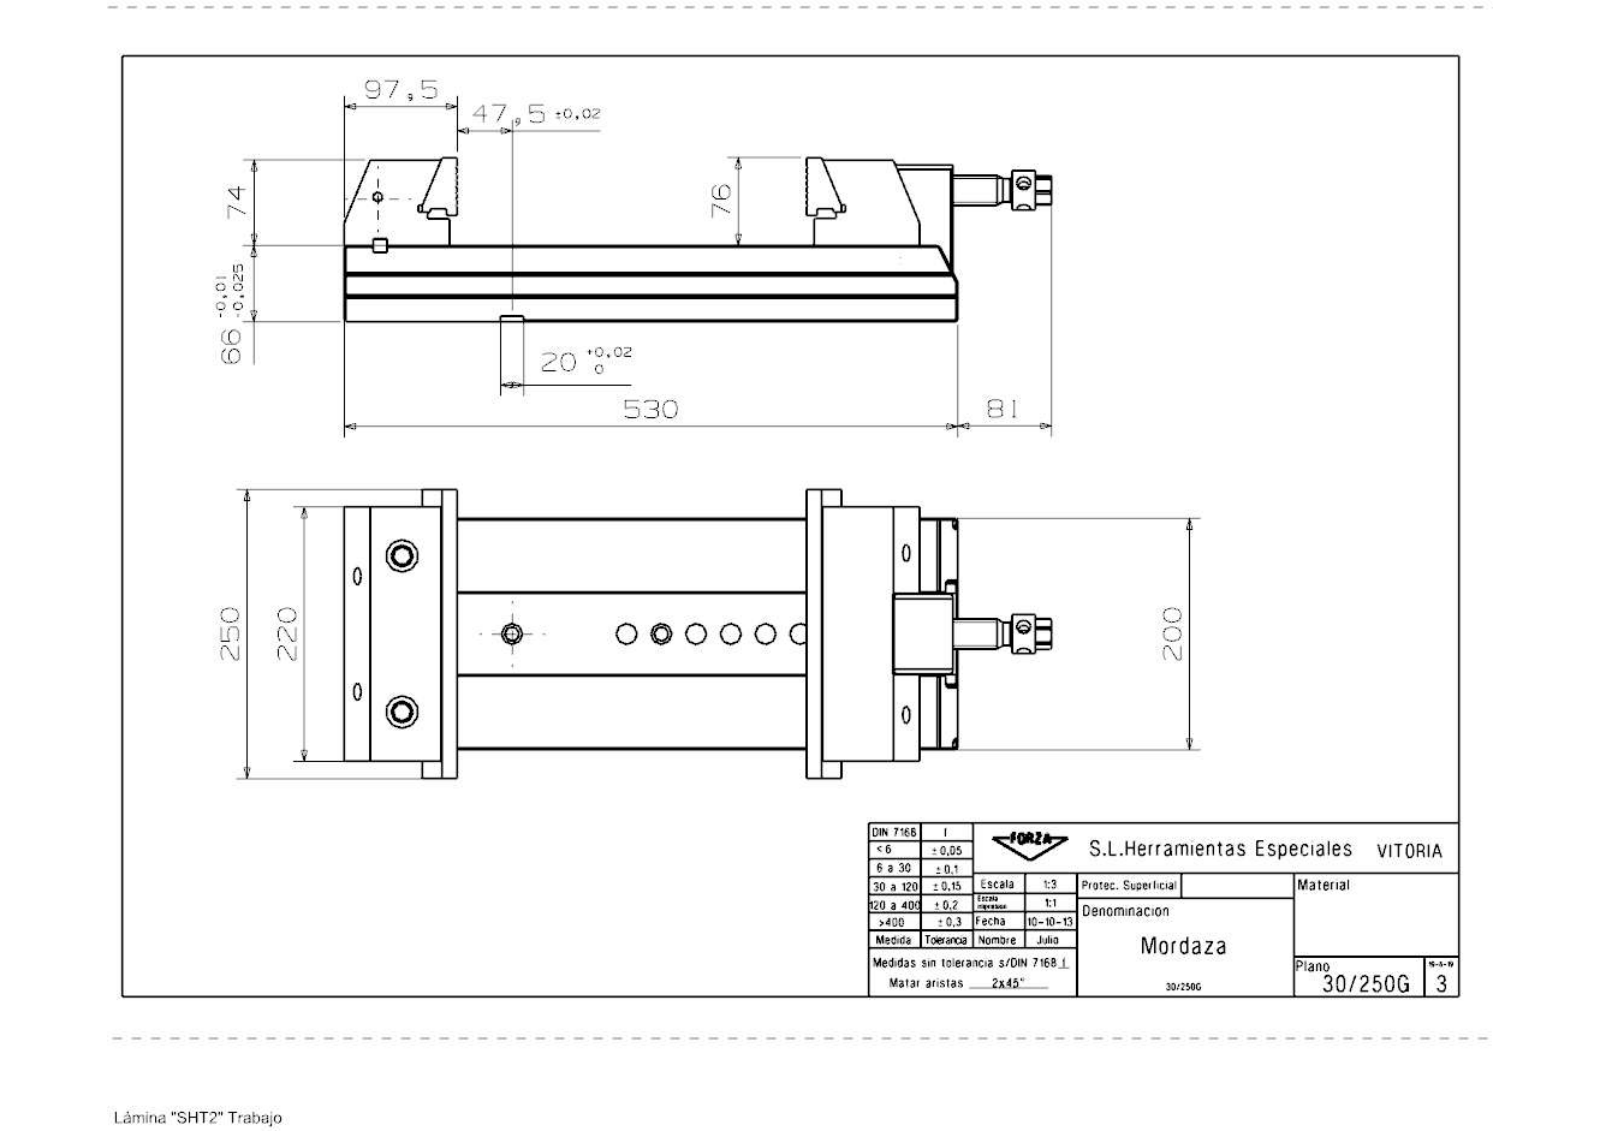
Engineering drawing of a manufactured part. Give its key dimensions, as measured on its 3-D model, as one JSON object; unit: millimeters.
{"part_name": "30_250G_Mordaza", "step_written_by": "SIEMENS PLM Software NX 7.5 (CONFIG_CONTROL_DESIGN)", "units": "millimeters", "bodies": {"solids": 13, "faces": 633, "planar": 472, "cylindrical": 103, "other": 58}, "overall_size": [615, 250, 140.05], "volume_mm3": 8157000, "surface_area_mm2": 756828, "round_holes": [[8.78, 5], [19, 5], [5.19, 4], [6.99, 4], [8.5, 4], [9.5, 4], [10.5, 4], [15, 4], [18, 4], [6, 3], [10.58, 3], [12.38, 3]], "round_bosses_or_shafts": [[34, 1], [33.8, 1], [26, 1], [20, 1], [16.5, 1]], "partial_cylinders_radius": [[10, 8], [6.5, 2], [9, 1], [10.5, 1], [12.5, 1], [13.25, 1]], "face_to_face_distances": [66, 65, 33.7, 32.3, 1.5, 64.5, 32.2, 10, 145, 0.5], "hole_center_spacings": [145.42, 20, 28, 46.32, 50, 72, 100, 117.5]}
